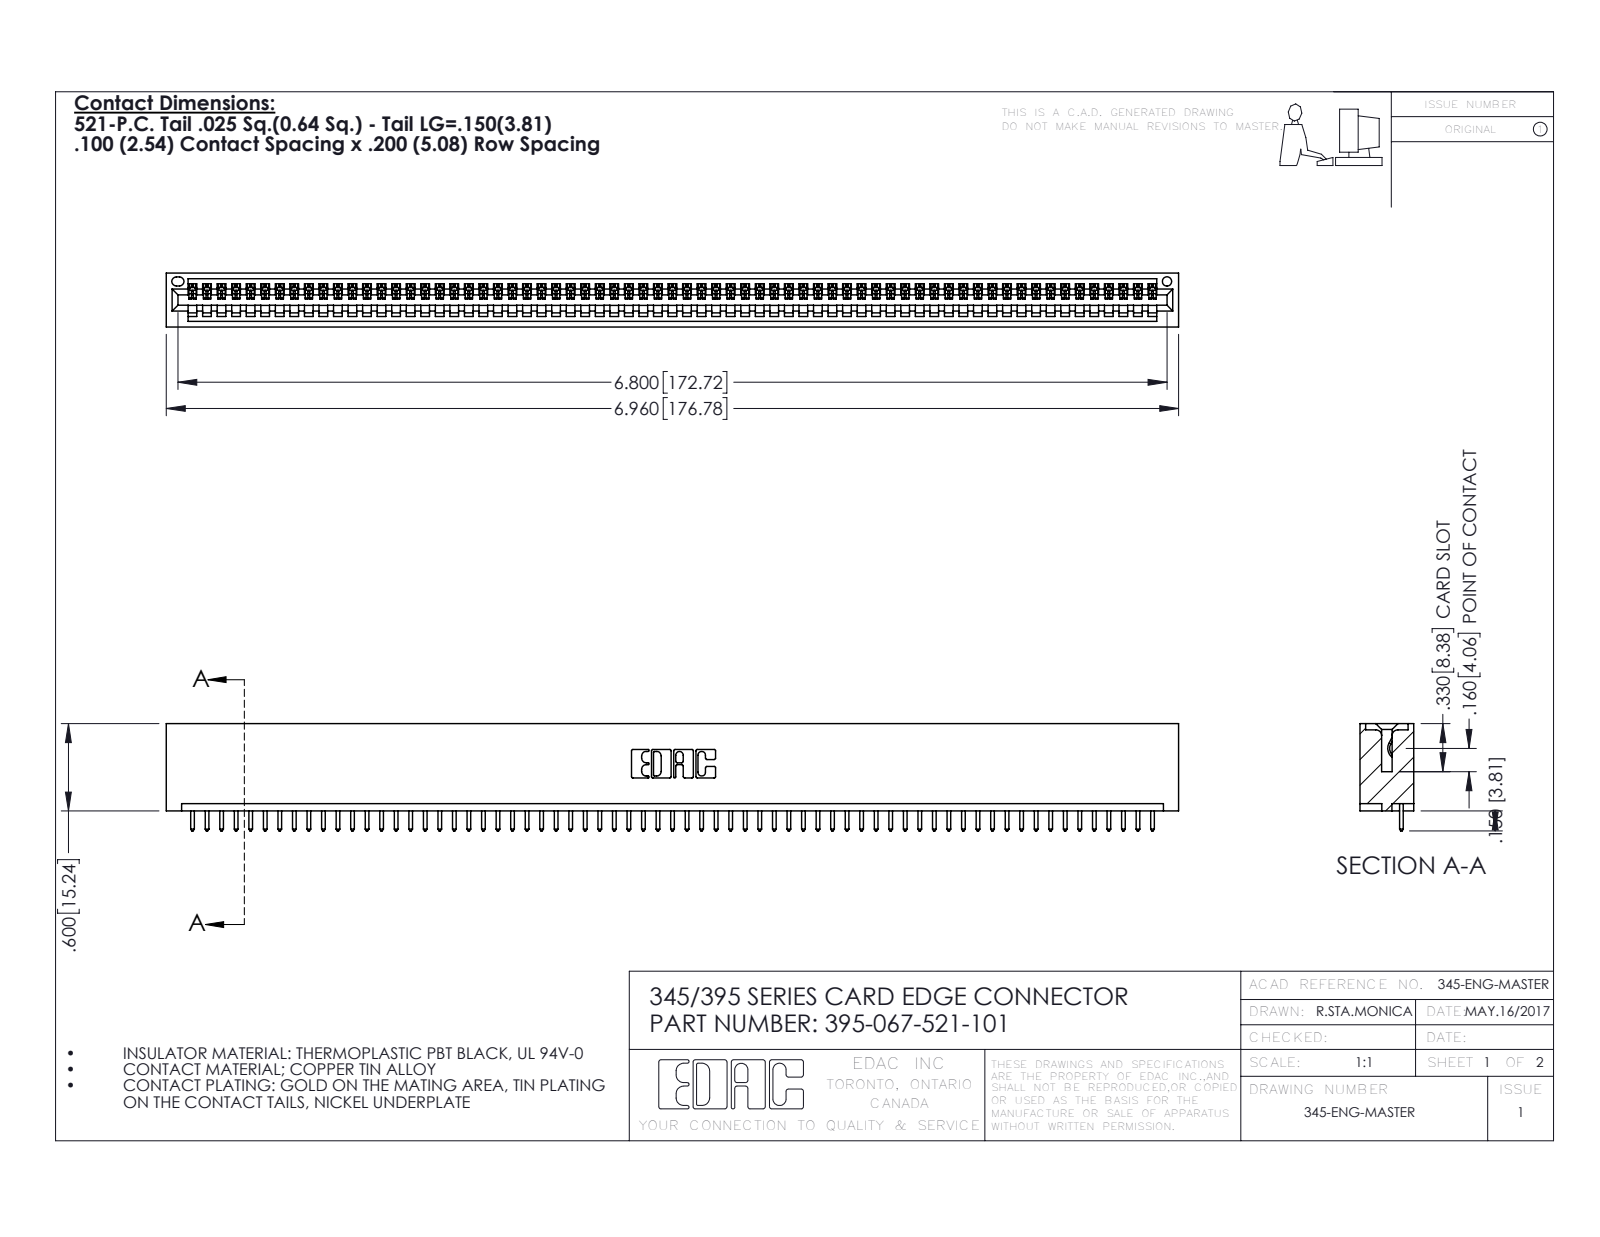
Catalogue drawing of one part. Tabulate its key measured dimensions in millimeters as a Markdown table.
| quantity | value |
| --- | --- |
| part name | 395-067-521-101; 345 Part_No Mounting Lugs; 345-292-001_345-293-121 |
| STEP written by | SolidWorks 2016 (CONFIG_CONTROL_DESIGN) |
| units | millimeters |
| bodies | 68 solids, 4004 faces (2756 planar, 1248 cylindrical, 0 other) |
| overall size | 176.8 × 18.7 × 9.4 |
| volume | 17 390 mm³ |
| surface area | 22 900 mm² |
| round holes (diameter × count) | 1.6 × 1 |
| partial cylindrical surfaces (radius × count) | 0.2 × 134, 0.3 × 134, 0.3 × 22, 0.2 × 6, 0.8 × 6, 0.7 × 3, 0.8 × 2, 1 × 2 |
| main face-to-face distances | 7.6, 1.8, 9.4, 5.1, 2.5, 6.9, 0.6, 5.7, 3.8, 1.8 |
